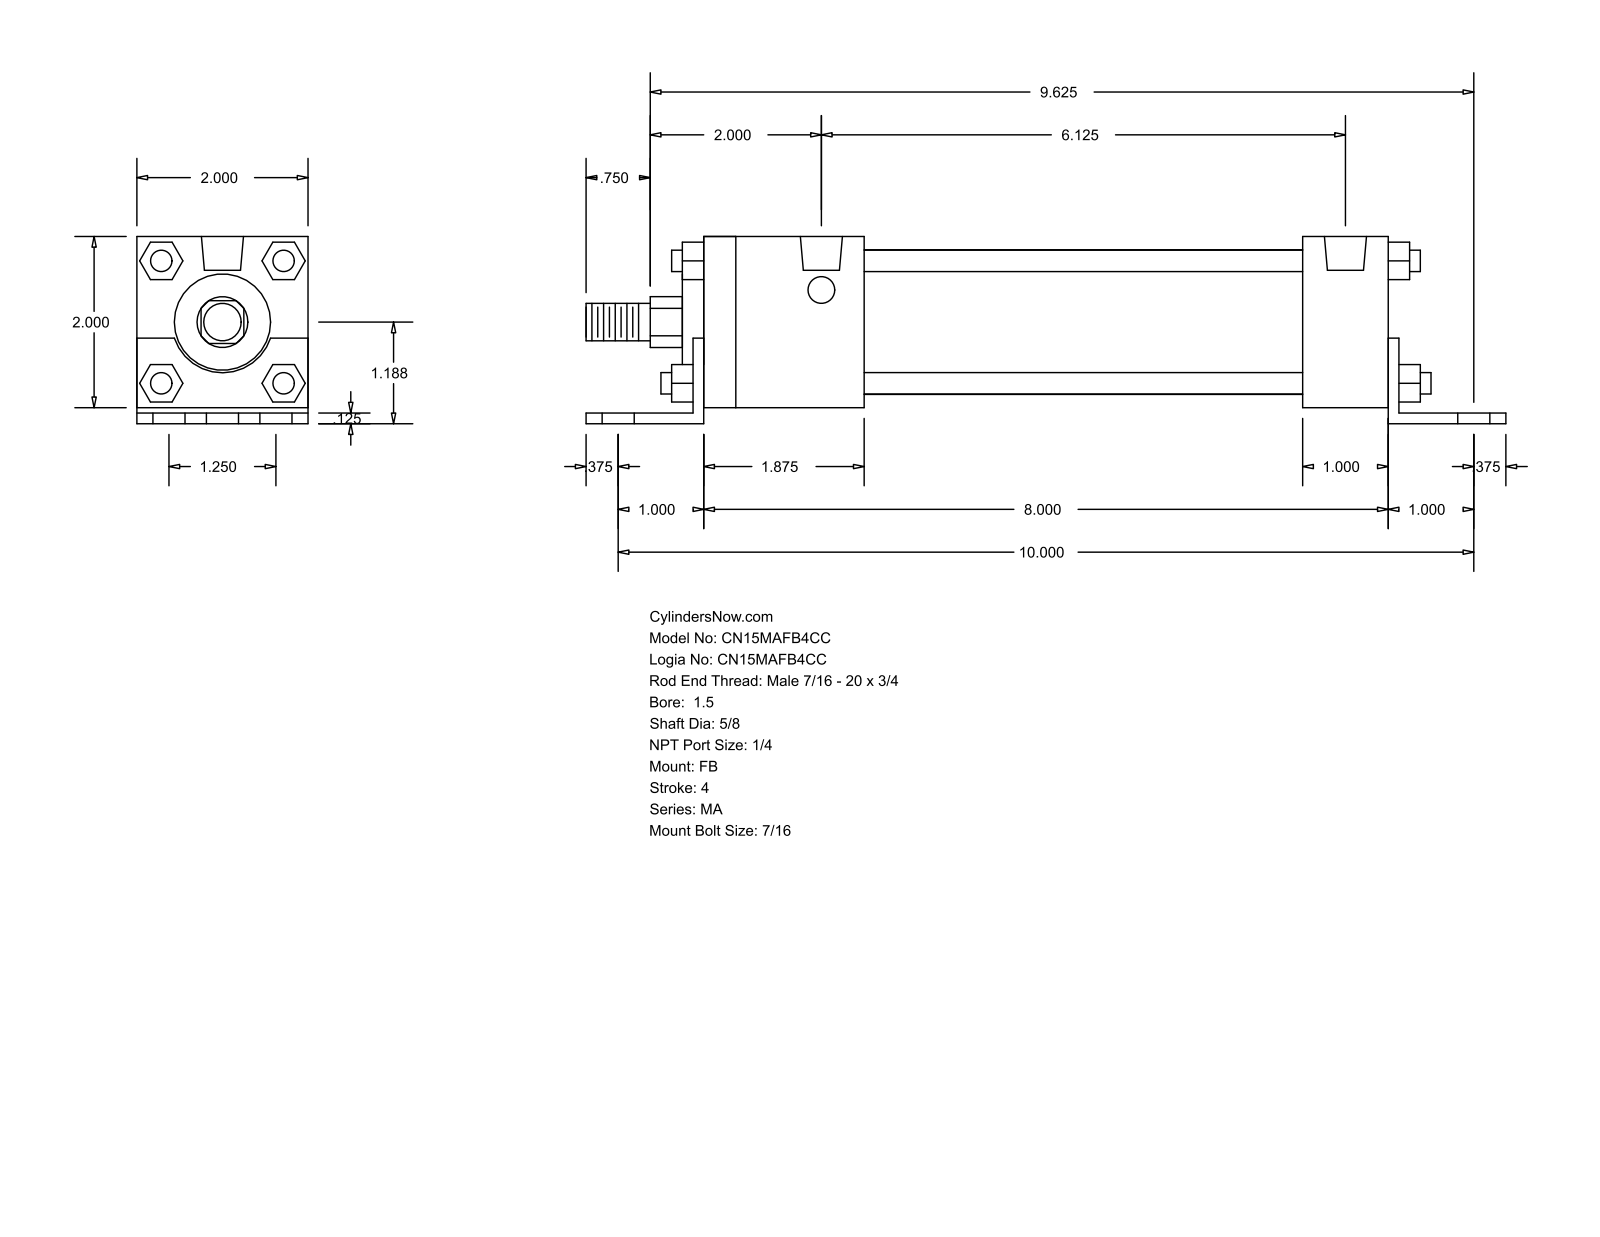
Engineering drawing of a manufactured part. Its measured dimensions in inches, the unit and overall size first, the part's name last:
Units: inches
Overall size (bounding box): 10.75 × 2.187 × 2
Round holes (diameter × count): ⌀0.437 ×6, ⌀0.313 ×4, ⌀0.492 ×2
Round bosses / shafts (diameter × count): ⌀0.25 ×4, ⌀1.69 ×1, ⌀1.125 ×1, ⌀0.625 ×1, ⌀0.437 ×1
Partial cylindrical surfaces — rounded edges, fillets, slot ends (radius × count): R0.297 ×1, R0.593 ×1
Main face-to-face distances: 2, 0.125, 0.187, 2.187, 0.063, 2.063, 0.125, 8.125, 0.25, 8
Hole centre spacings: 0.625, 10.02, 10, 1.25, 1.625, 2.456, 6.125, 7.65
Bodies: 0 solids, 140 faces (105 planar, 35 cylindrical, 0 other)
Part name (STEP PRODUCT): MA_FB__0150_0.625
STEP written by: GSSL Pune (CONFIG_CONTROL_DESIGN)
